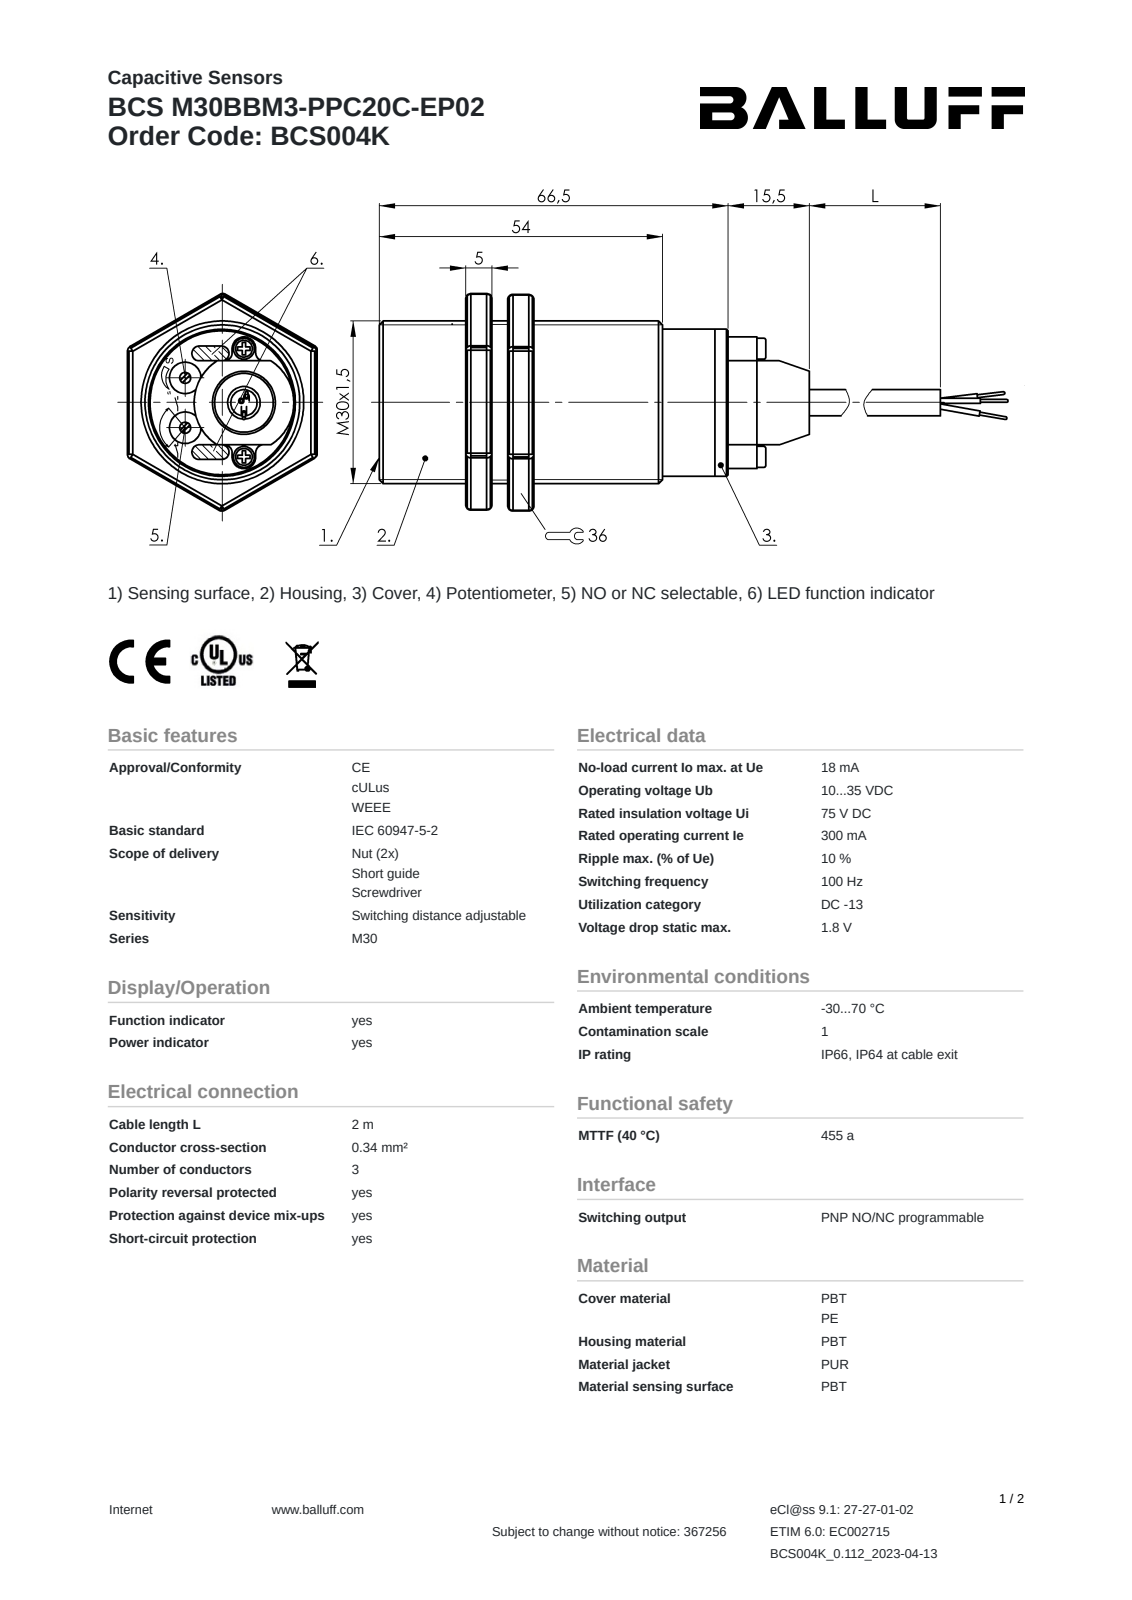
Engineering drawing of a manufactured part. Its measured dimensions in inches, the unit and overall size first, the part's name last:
Units: inches
Overall size (bounding box): 3.76 × 1.637 × 1.417
Round holes (diameter × count): ⌀0.098 ×2, ⌀0.197 ×2, ⌀0.244 ×1, ⌀1.117 ×1
Round bosses / shafts (diameter × count): ⌀0.157 ×2, ⌀1.181 ×1, ⌀1.102 ×1, ⌀1.094 ×1, ⌀0.197 ×1
Partial cylindrical surfaces — rounded edges, fillets, slot ends (radius × count): R0.05 ×4, R0.059 ×4, R0.089 ×2, R0.362 ×1, R0.374 ×1
Main face-to-face distances: 0.315, 0.197, 1.417, 1.161, 0.965, 1.28, 0.512, 1.476, 0.118, 1.142
Hole centre spacings: 0.333, 0.479, 0.165, 0.374
Volume: 3.304 in³ · Surface area: 19.33 in²
Bodies: 3 solids, 141 faces (79 planar, 27 cylindrical, 35 other)
Part name (STEP PRODUCT): BCS004K
STEP written by: SolidWorks 2021 (AUTOMOTIVE_DESIGN)
